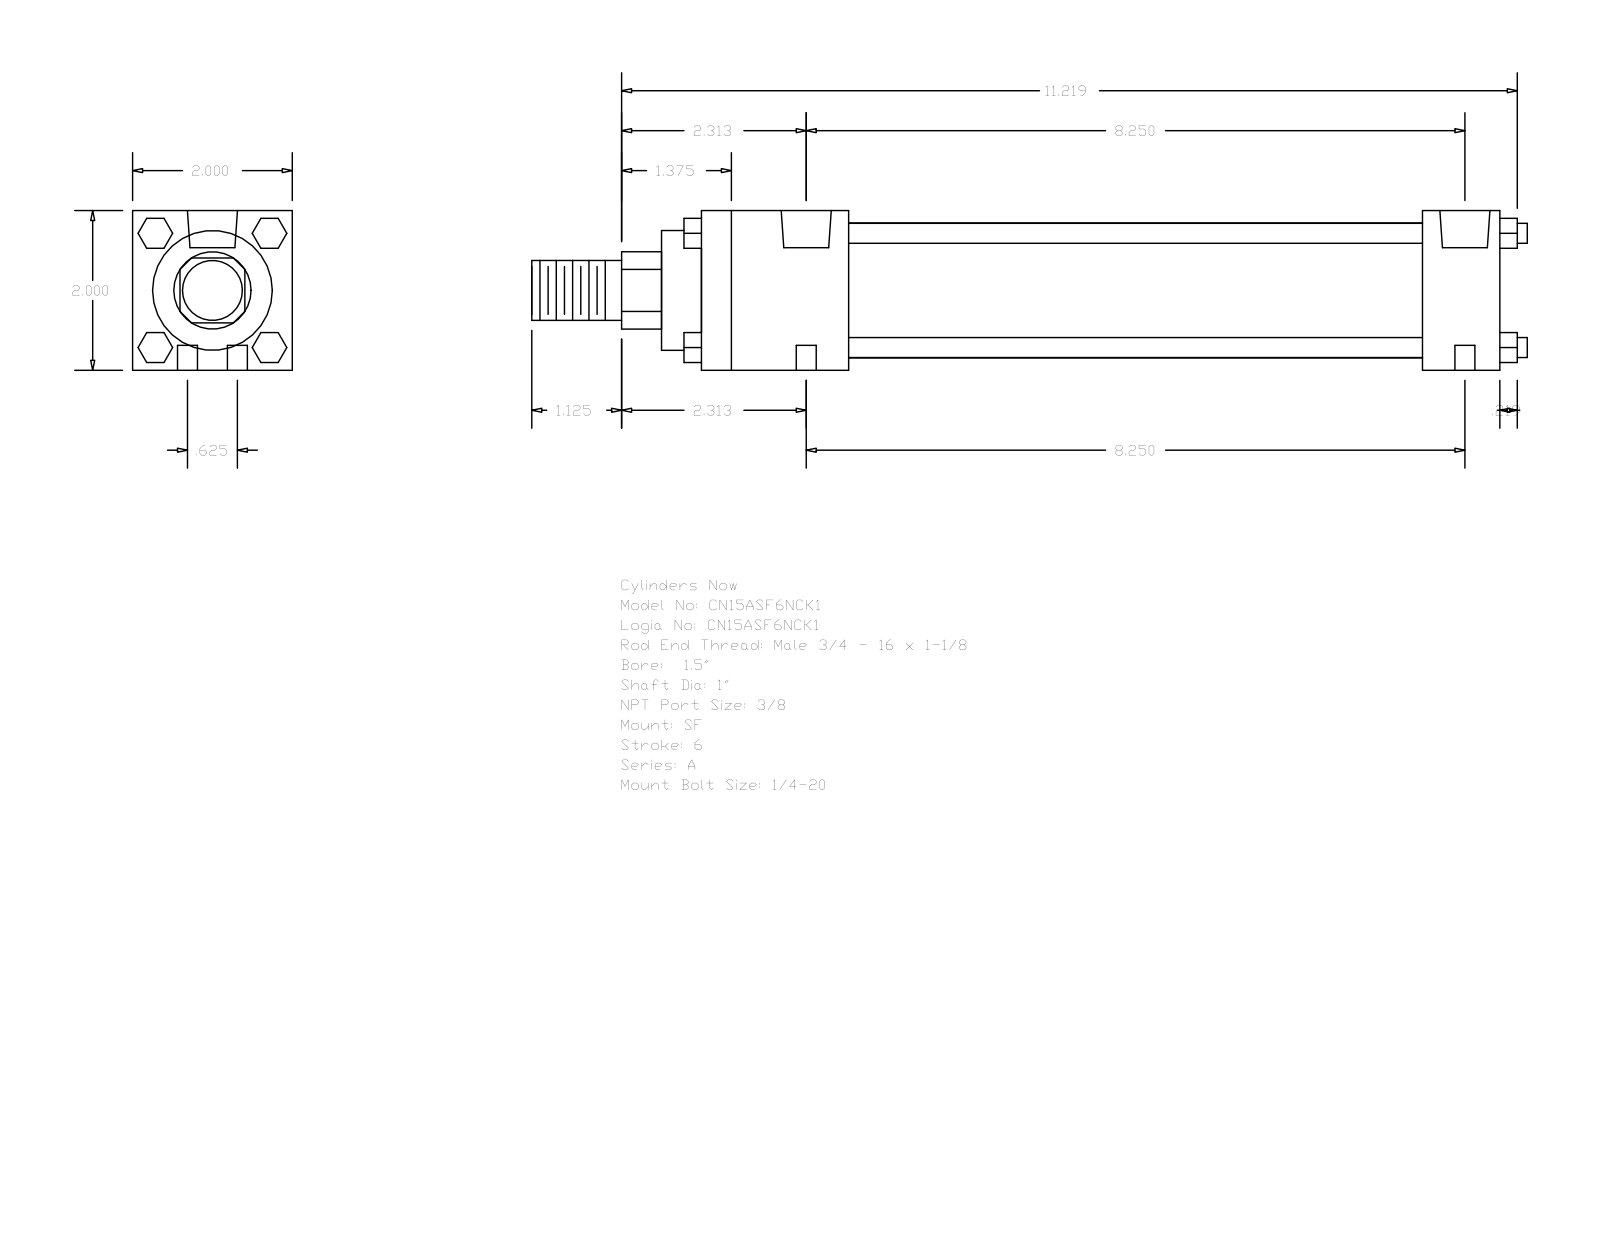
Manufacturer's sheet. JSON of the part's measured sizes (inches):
{"part_name": "A_SF__0150_1", "step_written_by": "GSSL Pune (CONFIG_CONTROL_DESIGN)", "units": "inches", "bodies": {"solids": 0, "faces": 124, "planar": 94, "cylindrical": 30, "other": 0}, "overall_size": [12.469, 2, 2], "round_holes": [[0.25, 4], [0.219, 2], [0.627, 2]], "round_bosses_or_shafts": [[0.25, 4], [1.69, 1], [1.5, 1], [1, 1], [0.75, 1]], "partial_cylinders_radius": [[0.484, 1]], "face_to_face_distances": [2, 10, 1.844, 9.031, 7.187, 8.156, 0.969, 0.5, 2.344, 9.531], "hole_center_spacings": [0.313, 8.256, 8.25, 0.625, 8.274, 7.937]}
